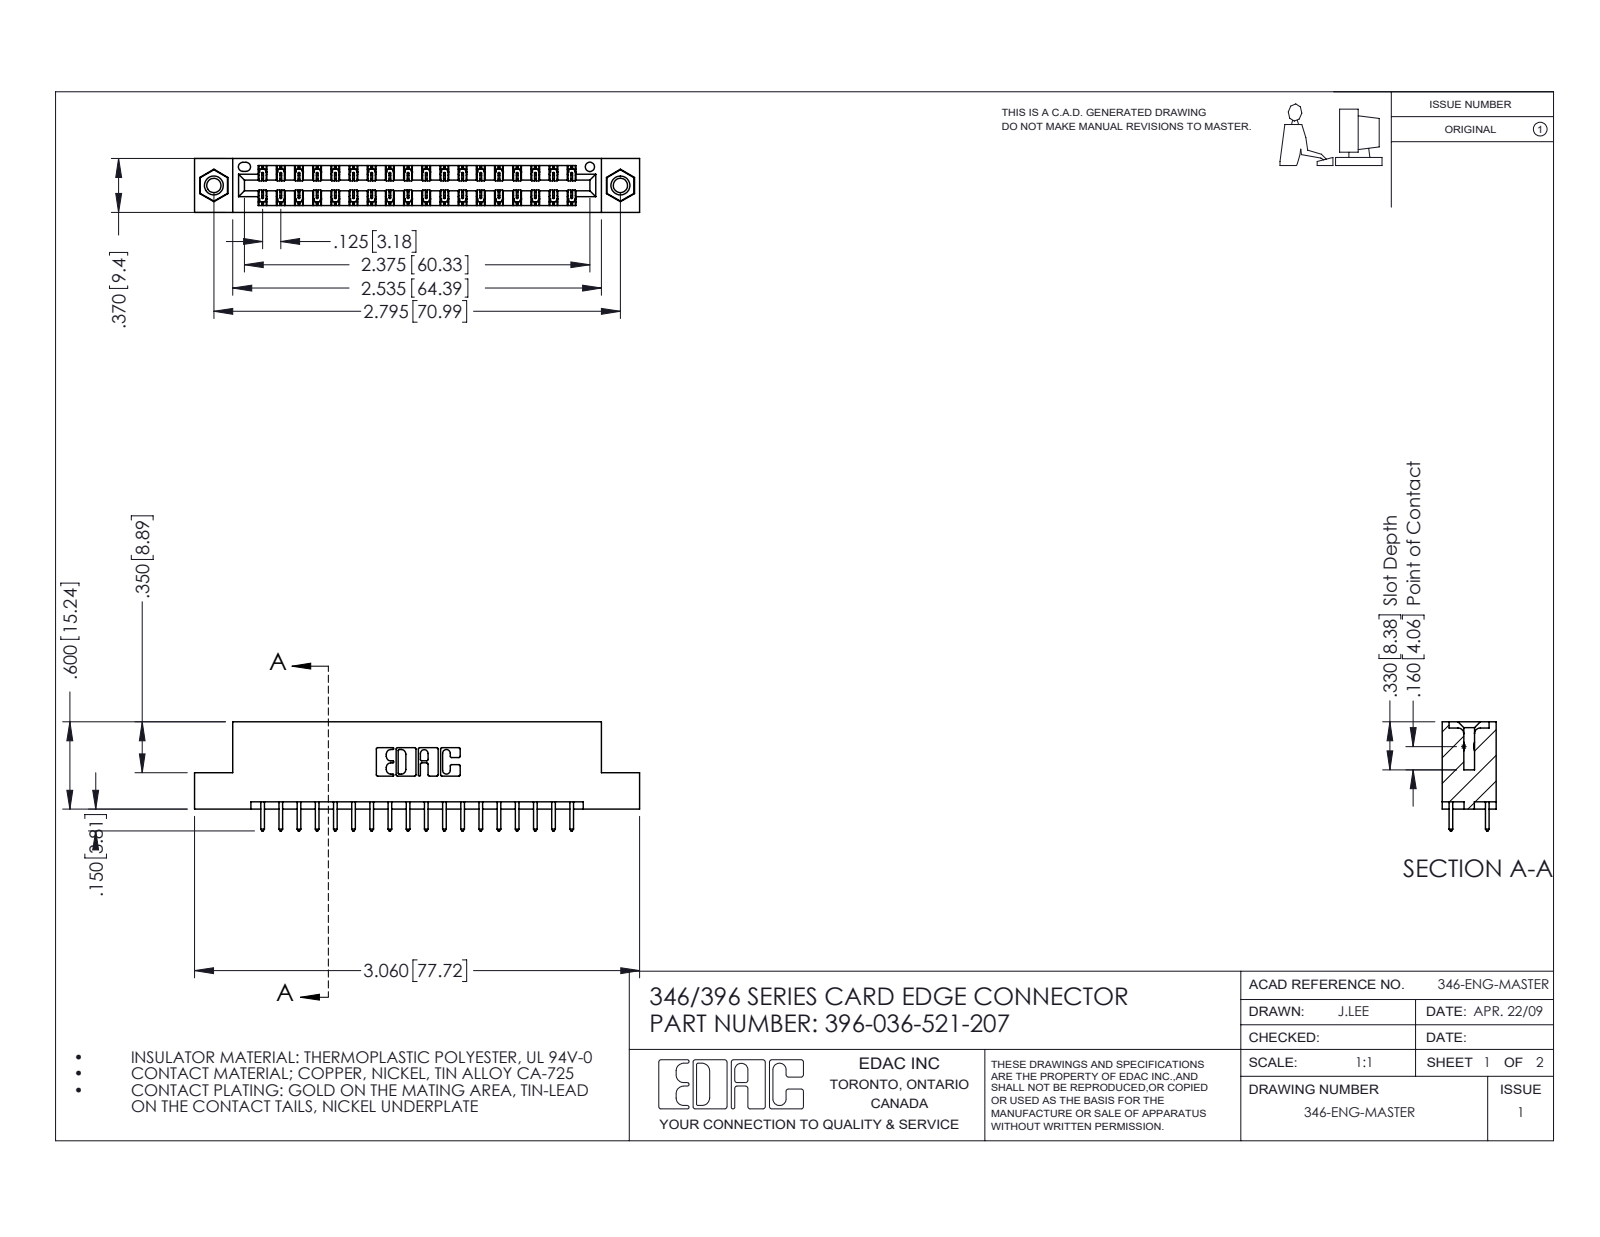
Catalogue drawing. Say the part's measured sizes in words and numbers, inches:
The part is named "346 Part_Flush Mounting Lugs - 0.156 Dia-TI; 396-036-521-207; 345-250-001_345-250-005-103; 345-292-001_345-293-121". Its 3-D file was written by "SolidWorks 2016 (CONFIG_CONTROL_DESIGN)". It is 39 solids with 2054 faces: 1368 planar, 670 cylindrical and 16 other. Overall it measures 3.06 by 0.75 by 0.37 inches. Its volume is 0.449 cubic inches and its surface area 15 square inches. Round holes: 2 of diameter 0.098, 2 of diameter 0.125, 2 of diameter 0.156, 1 of diameter 0.064. Round bosses or shafts: 2 of diameter 0.155. Partial cylindrical surfaces (rounded edges, fillets, slot ends): 54 of radius 0.006, 36 of radius 0.01, 22 of radius 0.01, 6 of radius 0.007, 6 of radius 0.031, 3 of radius 0.026, 2 of radius 0.014, 2 of radius 0.022. The main face-to-face distances are 0.048, 0.322, 0.25, 0.37, 0.072, 0.298, 0.025, 0.275, 0.148, 0.222. The hole center spacings are 0.246, 2.588, 2.795.
